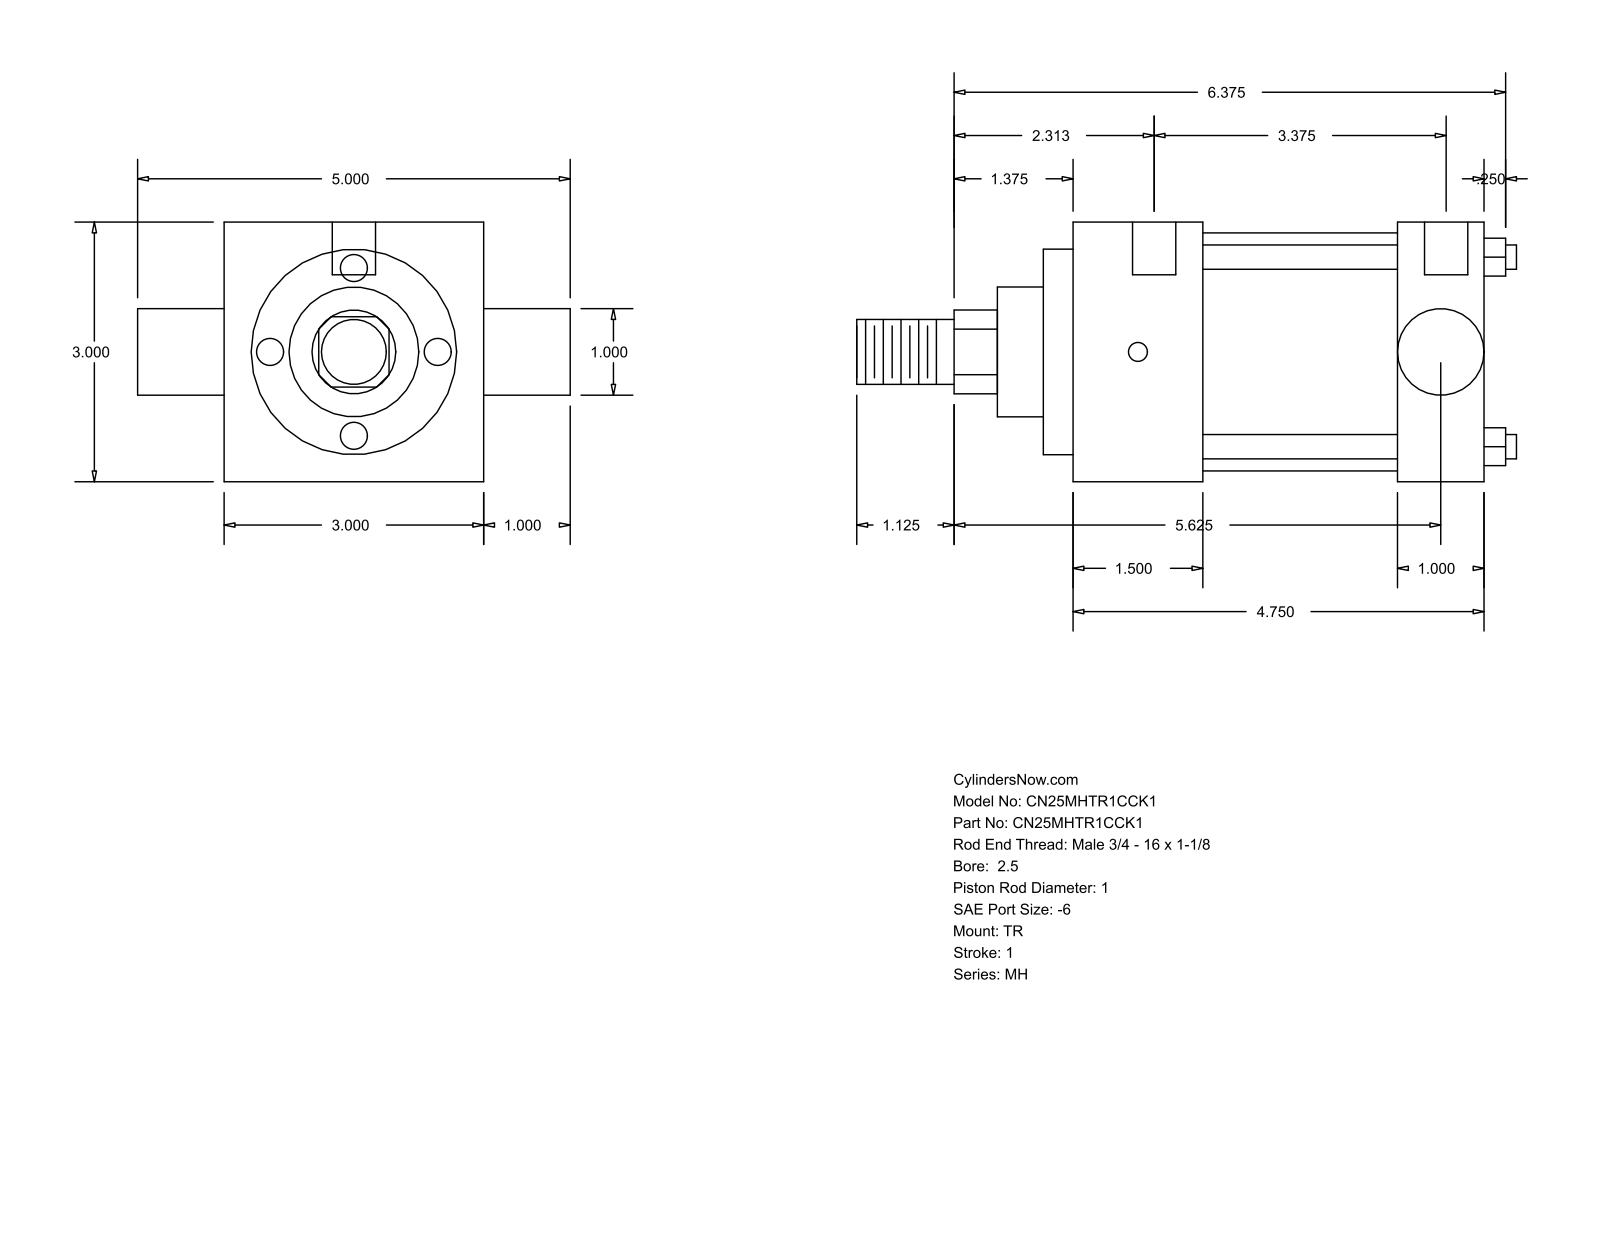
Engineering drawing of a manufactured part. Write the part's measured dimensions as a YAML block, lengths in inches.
part_name: "MH_TR__0250_1"
step_written_by: "GSSL Pune (CONFIG_CONTROL_DESIGN)"
units: inches
bodies: {solids: 0, faces: 86, planar: 61, cylindrical: 25, other: 0}
overall_size: [7.625, 5, 3]
round_holes:
  - {diameter: 0.219, count: 3}
  - {diameter: 0.5, count: 2}
round_bosses_or_shafts:
  - {diameter: 0.281, count: 4}
  - {diameter: 2.75, count: 1}
  - {diameter: 2.375, count: 1}
  - {diameter: 1.5, count: 1}
  - {diameter: 1, count: 1}
  - {diameter: 0.998, count: 1}
  - {diameter: 0.75, count: 1}
partial_cylinders:
  - {radius: 0.484, count: 1}
face_to_face_distances: [3, 4.75, 1, 1.5, 3.25, 3.75, 2.25, 0.344, 1.844, 4.094]
hole_center_spacings: [0.125, 0.187, 3.375, 3.5, 3.562, 3.687]
